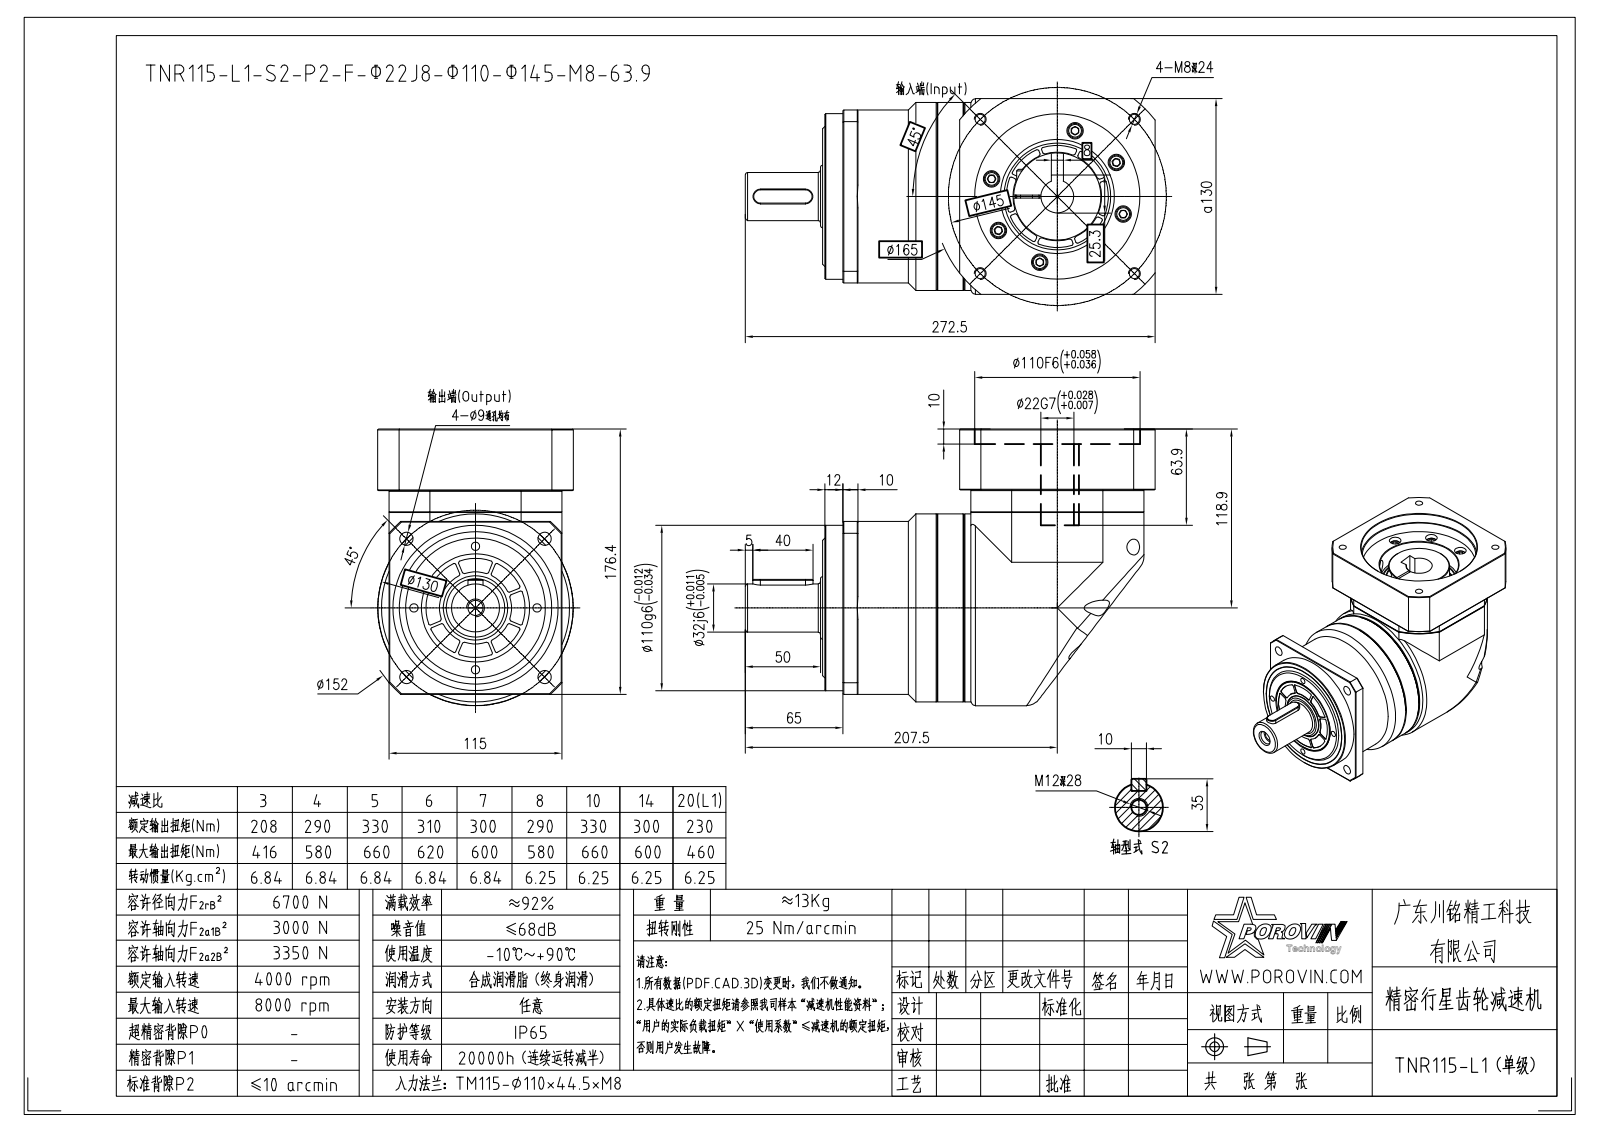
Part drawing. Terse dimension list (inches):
name: SPRING_LOCK_WASHERS--NORMAL_TYP; TM115_D110-M8-1450001; HEXAGON_SOCKET_HEAD_CAP_S-30884; TM1152280001 (+8 more)
written by: CREO PARAMETRIC BY PTC INC, 2020053 (CONFIG_CONTROL_DESIGN)
unit: in
bodies: 50 solids, 1418 faces (588 planar, 569 cylindrical, 261 other)
size: 10.728 × 7.24 × 5.118
volume: 178.7 in³; area: 550.2 in²
holes: 19× ⌀0.263, 13× ⌀0.256, 12× ⌀0.433, 8× ⌀0.197, 7× ⌀0.413, 6× ⌀0.26, 5× ⌀0.268, 4× ⌀0.217, 4× ⌀0.354, 2× ⌀2.835, 1× ⌀0.335, 1× ⌀0.402
bosses: 19× ⌀0.394, 19× ⌀0.389, 19× ⌀0.236, 1× ⌀5.118, 1× ⌀4.921, 1× ⌀4.882, 1× ⌀4.528, 1× ⌀4.331
rounds: 64× R0.039, 3× R0.197, 2× R0.157, 1× R0.266, 1× R0.394, 1× R2.559, 1× R2.992, 1× R3.248
face distances: 0.709, 0.701, 0.587, 0.295, 4.823, 0.118, 2.181, 5.118, 0.787, 1.594
hole spacings: 1.781, 1.828, 2.254, 2.898, 1.431, 1.818, 1.87, 2.024
